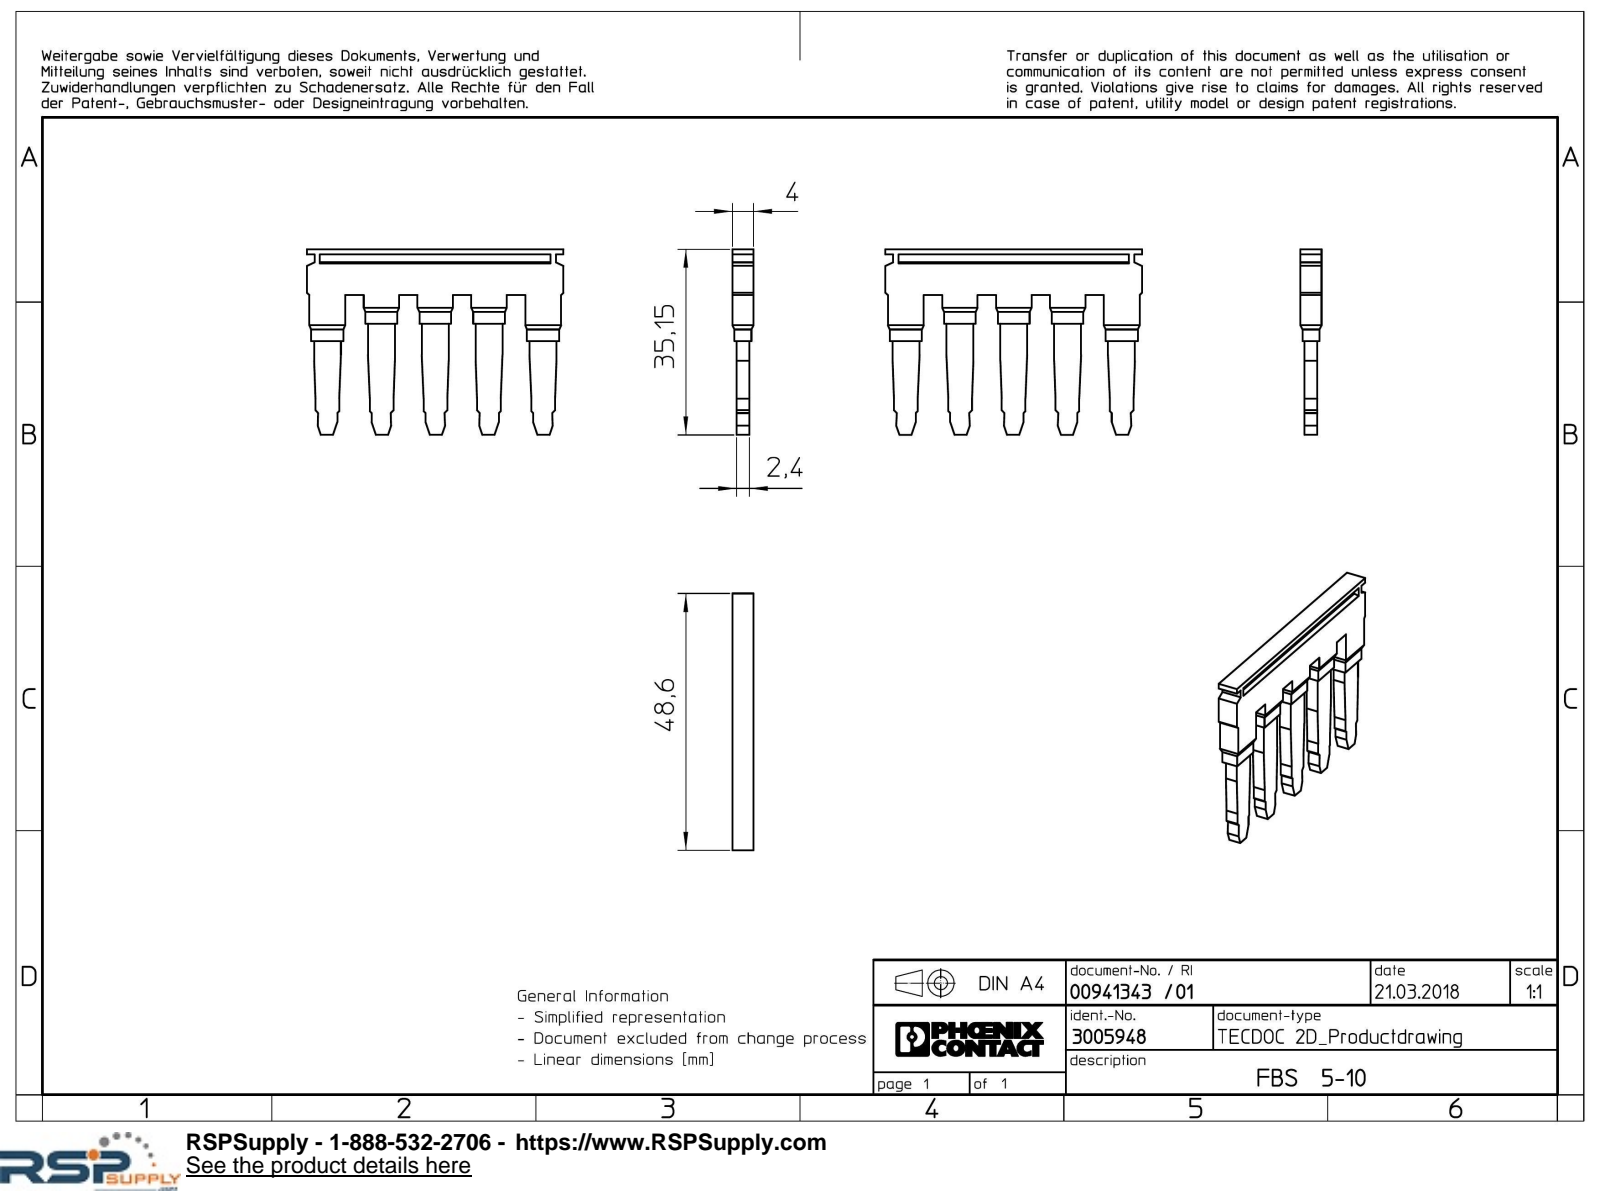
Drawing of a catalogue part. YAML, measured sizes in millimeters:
part_name: "FBS_5_10-select"
step_written_by: "Creo Elements/Direct Modeling 20.1A 29-Sep-2018 (C) Parametric Technology GmbH (AUTOMOTIVE_DESIGN)"
units: millimeters
bodies: {solids: 1, faces: 159, planar: 159, cylindrical: 0, other: 0}
overall_size: [48.6, 35.15, 4]
volume: 3406
surface_area: 3468
face_to_face_distances: [3.2, 0.8, 4, 2.4, 0.4, 1, 10.2, 3.6, 2.8, 3]
